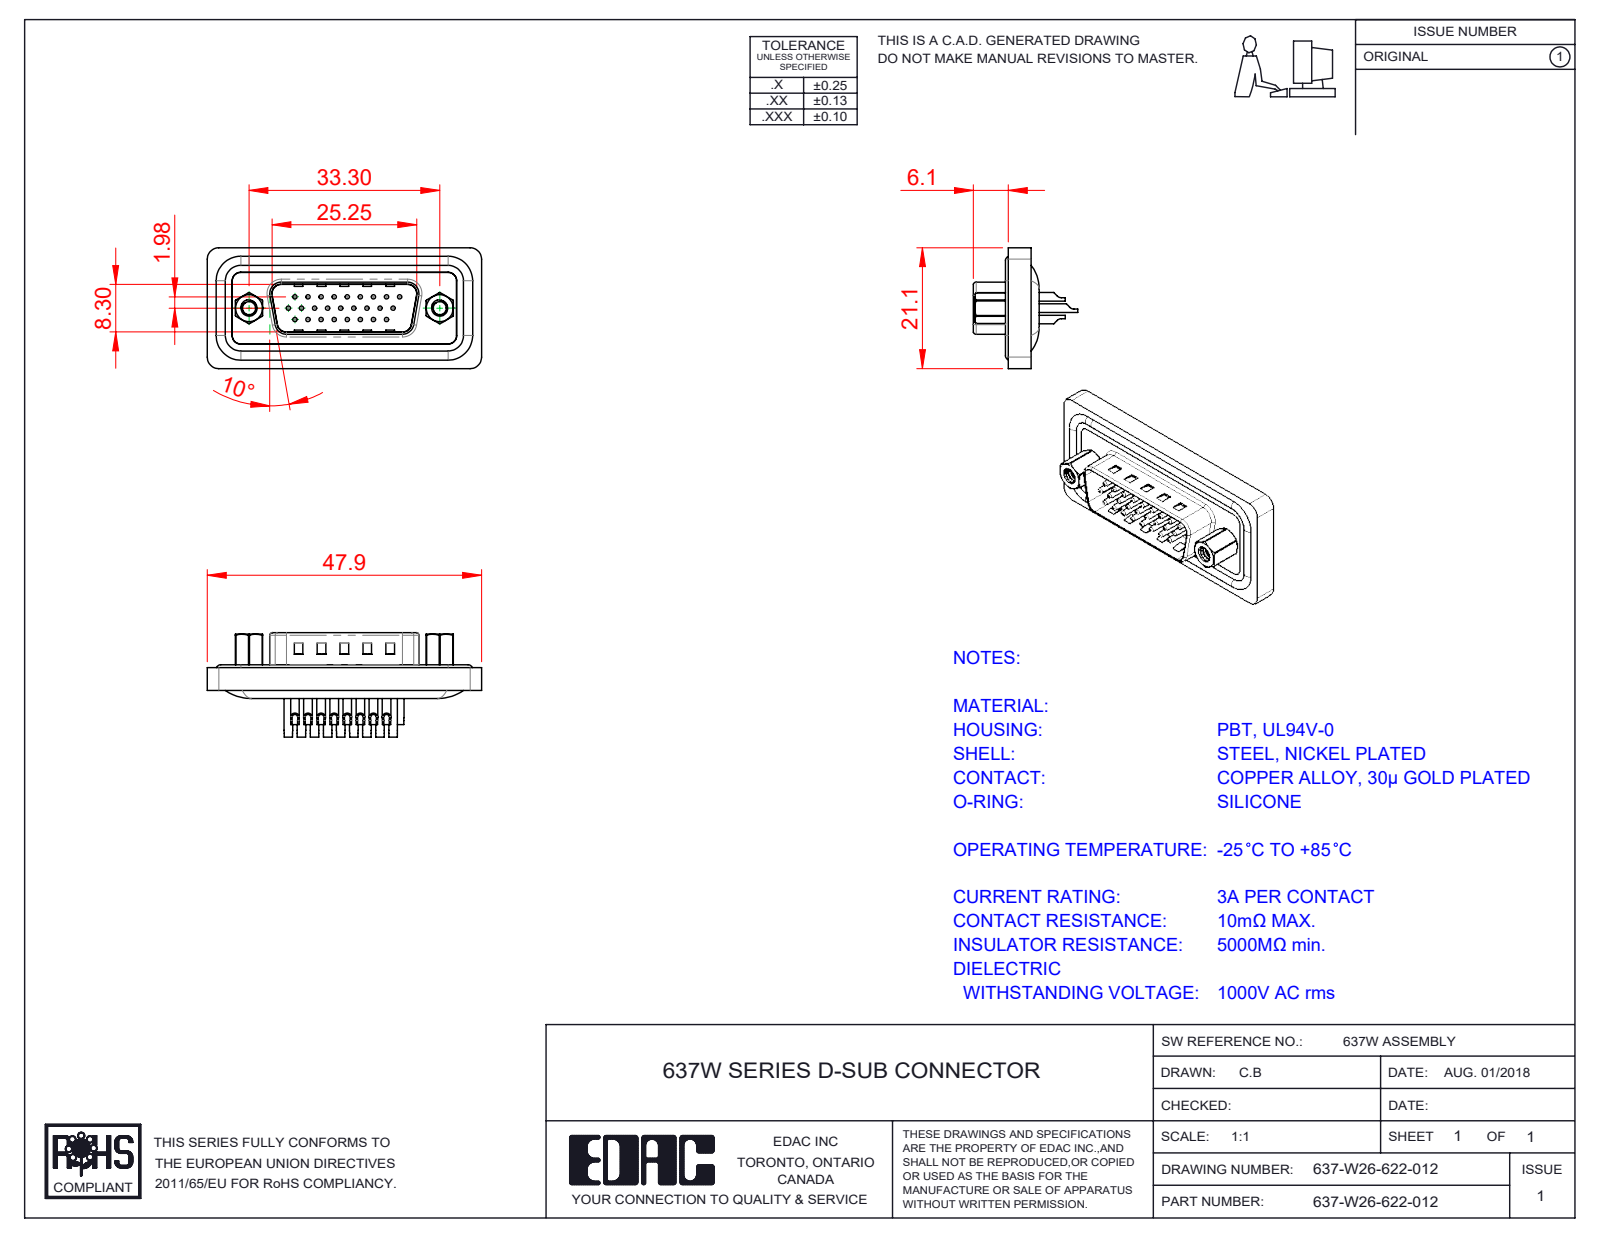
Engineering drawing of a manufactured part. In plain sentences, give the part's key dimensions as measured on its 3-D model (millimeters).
The part is named "637W Contact Row 2_22; 637W Waterproof Housing_26 Contacts; 637W Housing_26 Contacts; 637W Contact Row 3_22 (+5 more)". Its 3-D file was written by "SolidWorks 2016 (CONFIG_CONTROL_DESIGN)". It is 34 solids with 1496 faces: 407 planar, 680 cylindrical and 409 other. Overall it measures 47.89 by 21.1 by 18.25 millimeters. Its volume is 4 983 cubic millimeters and its surface area 9 119 square millimeters. Round holes: 26 of diameter 0.75, 26 of diameter 1, 26 of diameter 1.5, 26 of diameter 1.6, 26 of diameter 2, 2 of diameter 2.26, 2 of diameter 2.29, 2 of diameter 4, 2 of diameter 4.8, 2 of diameter 5. Round bosses or shafts: 26 of diameter 1.5, 4 of diameter 1.6, 2 of diameter 4.9, 2 of diameter 2.79, 1 of diameter 5. Partial cylindrical surfaces (rounded edges, fillets, slot ends): 16 of radius 2, 14 of radius 1.5, 8 of radius 0.5, 6 of radius 2.7, 4 of radius 0.9, 4 of radius 1.6, 4 of radius 4.3, 3 of radius 1. The main face-to-face distances are 0.4, 1.6, 1.1, 2.9, 2.5, 0.5, 5.65, 15.45, 0.75, 4. The hole center spacings are 3.96, 2.28, 4.57, 6.05, 2.29, 8.24, 6.86, 6.04.
